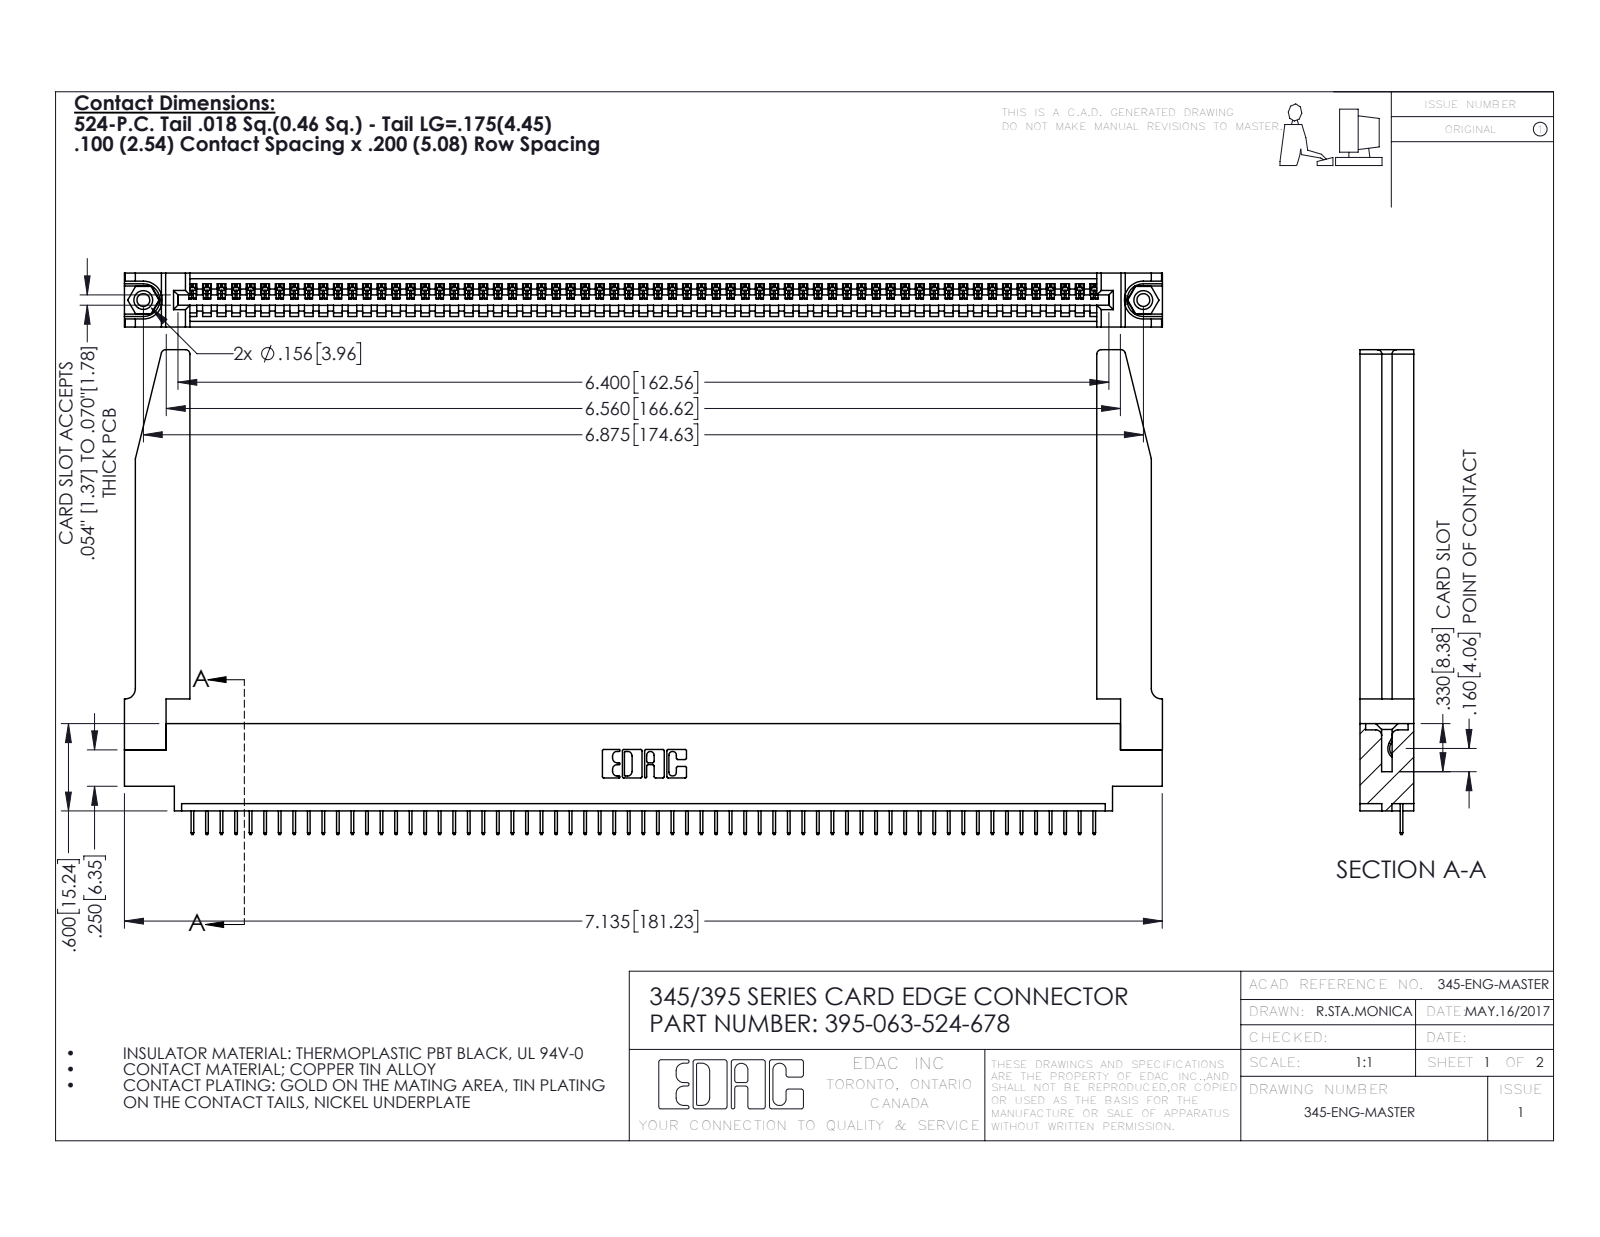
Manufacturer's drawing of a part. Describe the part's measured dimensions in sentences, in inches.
The part is named "345-292-001_345-293-124; 395-063-524-678; 345-250-001_345-250-001-102; 345-220-078_345-220-078 (+1 more)". Its 3-D file was written by "SolidWorks 2016 (CONFIG_CONTROL_DESIGN)". It is 68 solids with 4270 faces: 3124 planar, 1094 cylindrical and 52 other. Overall it measures 7.136 by 3.332 by 0.37 inches. Its volume is 1.513 cubic inches and its surface area 45.09 square inches. Round holes: 2 of diameter 0.089, 2 of diameter 0.125, 2 of diameter 0.156, 1 of diameter 0.064. Round bosses or shafts: 2 of diameter 0.155. Partial cylindrical surfaces (rounded edges, fillets, slot ends): 126 of radius 0.006, 22 of radius 0.01, 8 of radius 0.03, 6 of radius 0.007, 6 of radius 0.031, 3 of radius 0.026, 2 of radius 0.031, 2 of radius 0.04. The main face-to-face distances are 0.37, 0.072, 0.298, 0.098, 0.272, 0.025, 0.2, 0.225, 0.072, 0.148. The hole center spacings are 0.27, 6.639, 6.875.
